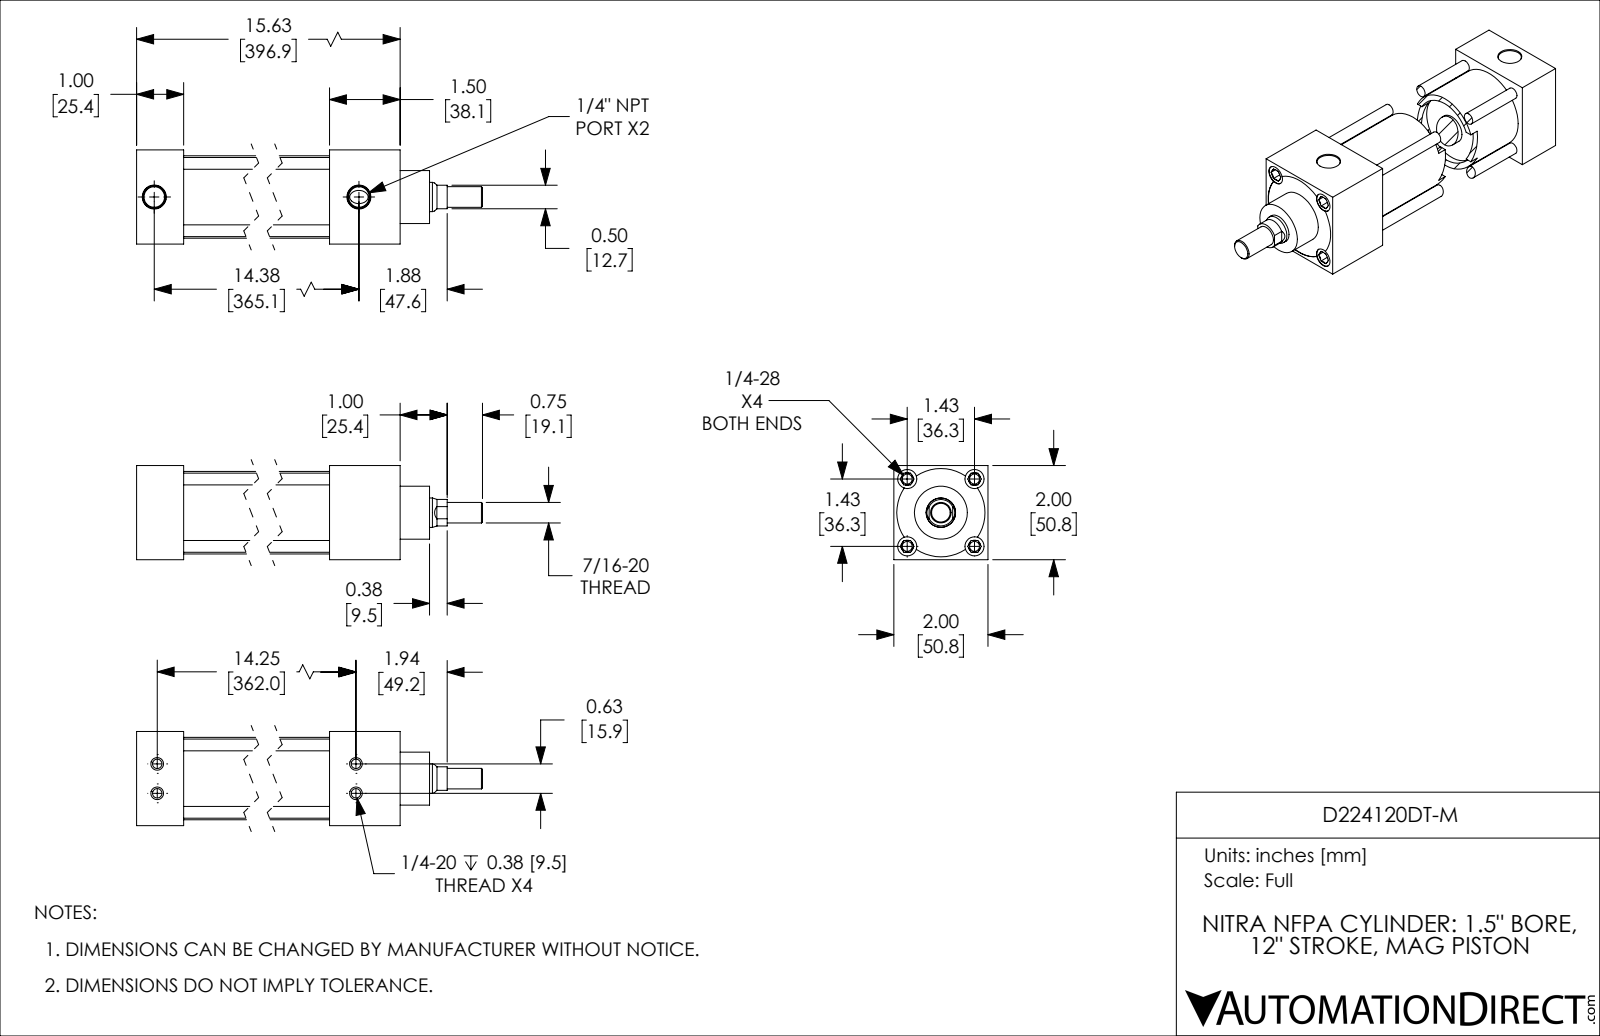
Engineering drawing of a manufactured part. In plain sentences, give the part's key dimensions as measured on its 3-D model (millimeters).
The part is named "D224120DT-M_PISTON_KK1; D224120DT-M; D224120DT-M_BODY". Its 3-D file was written by "SolidWorks 2019 (CONFIG_CONTROL_DESIGN)". It is 2 solids with 203 faces: 58 planar, 65 cylindrical and 80 other. Overall it measures 441.3 by 50.8 by 50.8 millimeters. Its volume is 440 300 cubic millimeters and its surface area 168 500 square millimeters. Round holes: 4 of diameter 5.1, 4 of diameter 5.4, 4 of diameter 10.3, 2 of diameter 11.1, 1 of diameter 15.9, 1 of diameter 38.1. Round bosses or shafts: 4 of diameter 6.4, 1 of diameter 44.5, 1 of diameter 38.1, 1 of diameter 28.6, 1 of diameter 15.8, 1 of diameter 11.1. Partial cylindrical surfaces (rounded edges, fillets, slot ends): 1 of radius 7.1, 1 of radius 23.8. The main face-to-face distances are 50.8, 25.4, 358.8, 333.4, 396.7, 371.3, 38, 28.6, 54, 304.8. The hole center spacings are 8.1, 25.7, 36.3, 15.9, 51.4, 362, 362.3, 363.6.
